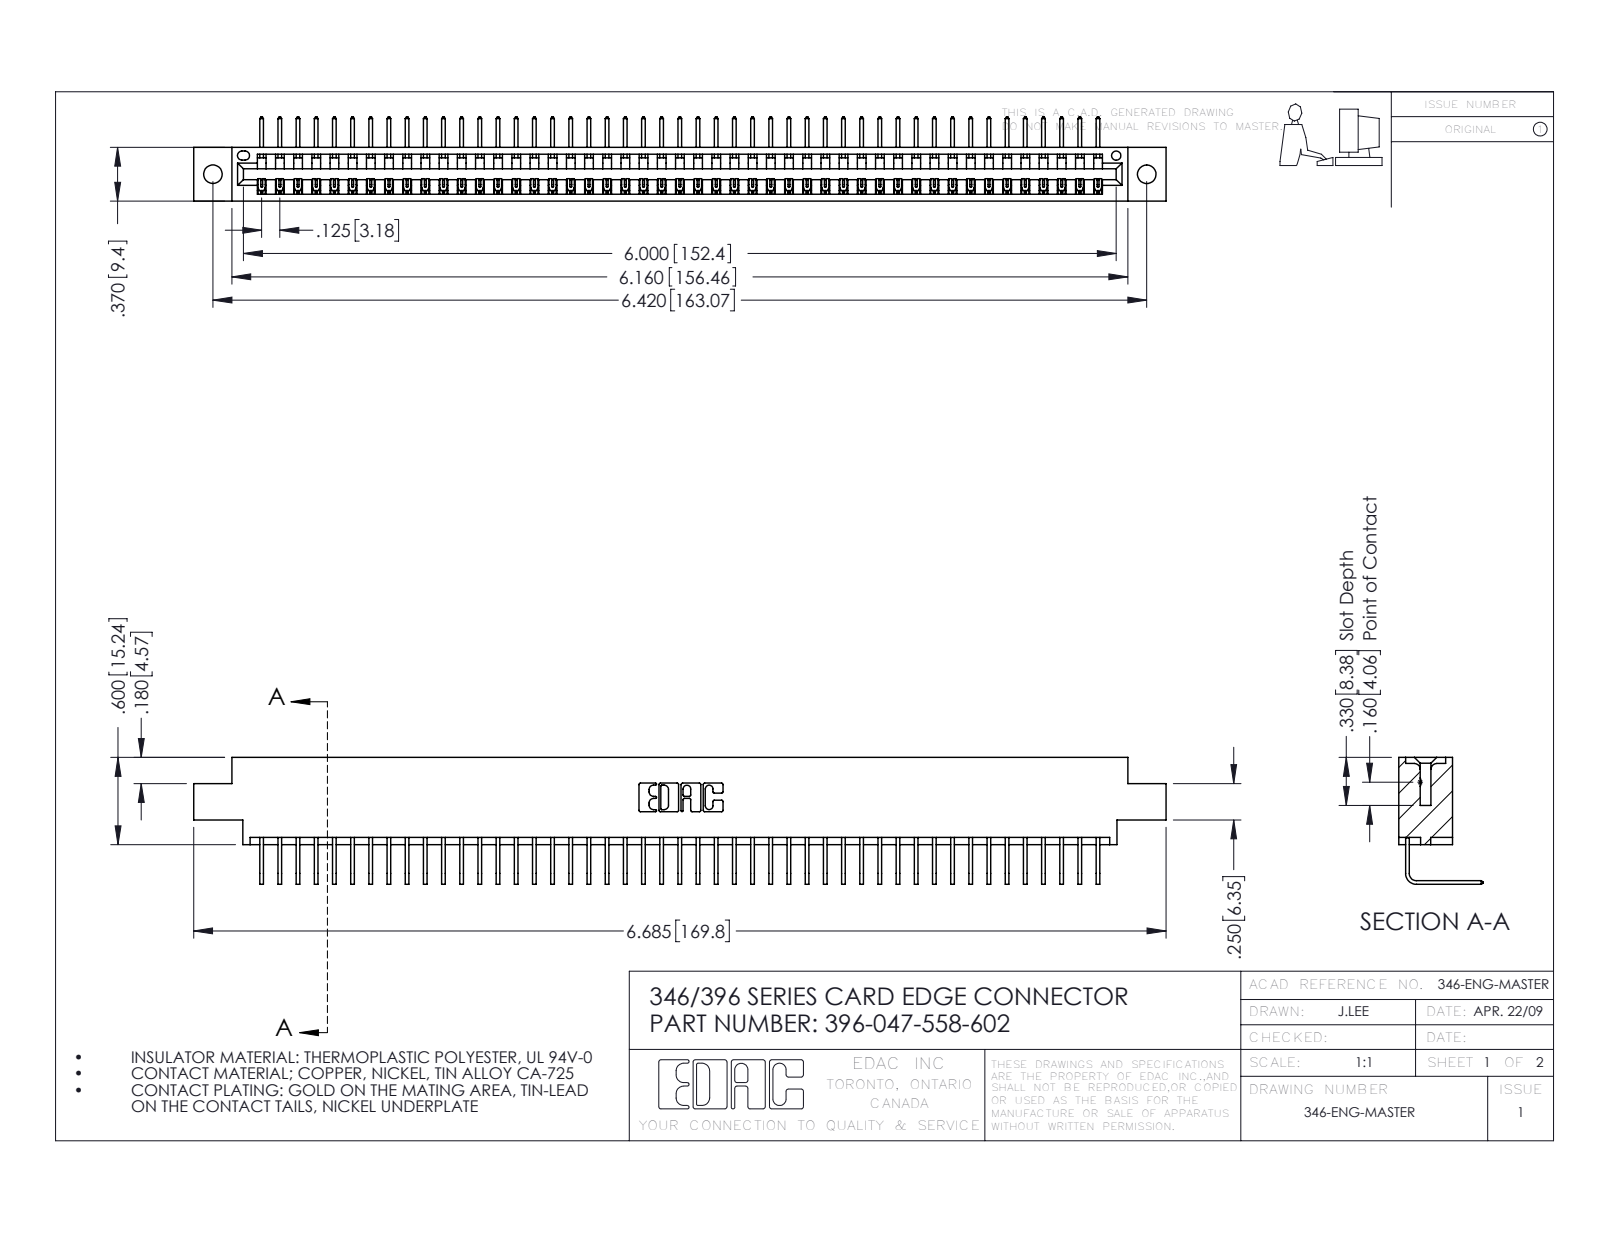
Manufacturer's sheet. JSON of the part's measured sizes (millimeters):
{"part_name": "345-292-001_558 Tail - 2; 346 Part_0.170 Offset - 0.128 Dia; 396-047-558-602", "step_written_by": "SolidWorks 2016 (CONFIG_CONTROL_DESIGN)", "units": "millimeters", "bodies": {"solids": 48, "faces": 2946, "planar": 2054, "cylindrical": 892, "other": 0}, "overall_size": [169.8, 22.2, 14.7], "volume_mm3": 16300, "surface_area_mm2": 21190, "round_holes": [[3.3, 2], [1.6, 1]], "partial_cylinders_radius": [[0.2, 94], [0.3, 22], [0.2, 6], [0.8, 6], [0.7, 3], [0.8, 2], [1, 2], [0.4, 1]], "face_to_face_distances": [8.2, 1.2, 9.4, 6.4, 7.6, 0.6, 1.8, 3.8, 5.6, 2.5], "hole_center_spacings": [6.2, 157.8, 163.1]}
